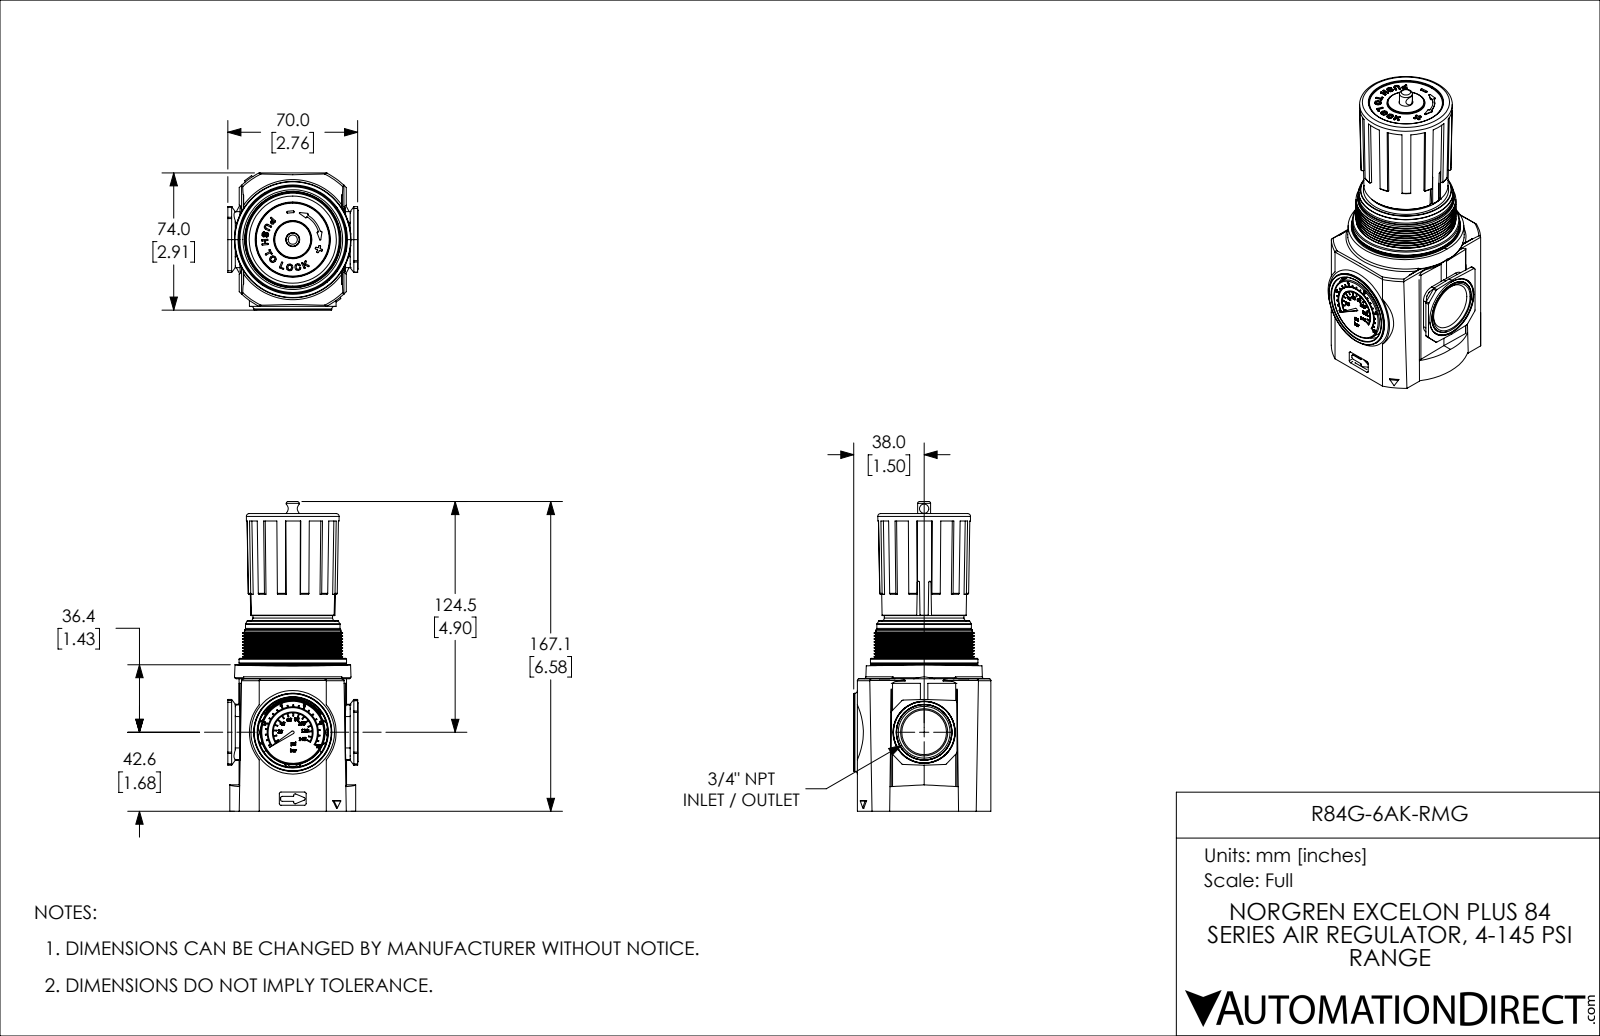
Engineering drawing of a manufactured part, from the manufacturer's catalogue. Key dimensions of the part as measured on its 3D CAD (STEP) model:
Part name (STEP PRODUCT): R84G-6AK-RMG
STEP written by: SolidWorks 2021 (CONFIG_CONTROL_DESIGN)
Units: inches
Bodies: 6 solids, 2246 faces (789 planar, 1065 cylindrical, 392 other)
Overall size (bounding box): 6.577 × 2.913 × 2.766
Volume: 27.77 in³ · Surface area: 175.1 in²
Round holes (diameter × count): ⌀0.177 ×2, ⌀0.059 ×1, ⌀0.197 ×1, ⌀0.222 ×1, ⌀1.319 ×1, ⌀2.323 ×1
Round bosses / shafts (diameter × count): ⌀0.299 ×2, ⌀0.157 ×2, ⌀2.283 ×1, ⌀2.119 ×1, ⌀2.047 ×1, ⌀2.026 ×1, ⌀2.008 ×1, ⌀1.732 ×1
Partial cylindrical surfaces — rounded edges, fillets, slot ends (radius × count): R0.028 ×48, R0.012 ×27, R0.039 ×26, R0.047 ×18, R0.03 ×16, R0.02 ×15, R0.004 ×14, R0.06 ×12
Main face-to-face distances: 2.638, 2.035, 0.602, 0.472, 2.508, 3.11, 4.156, 0.512, 3.683, 1.648
Hole centre spacings: 0.856, 1.713
